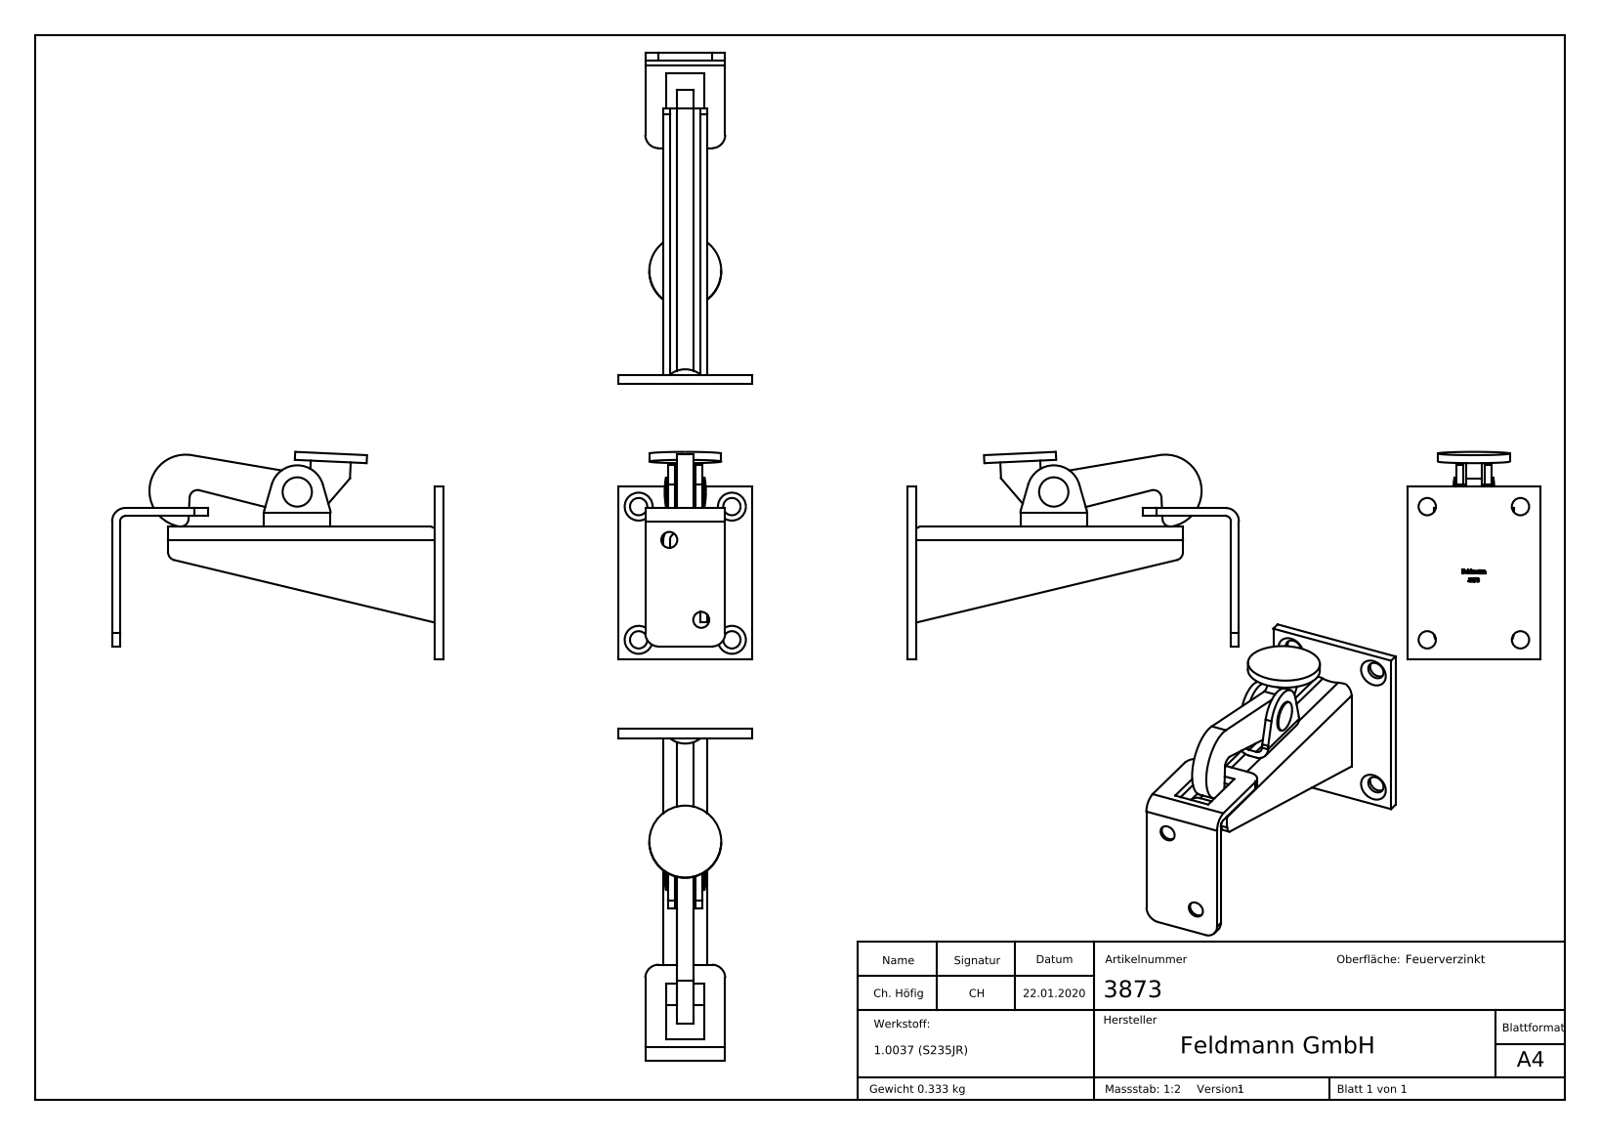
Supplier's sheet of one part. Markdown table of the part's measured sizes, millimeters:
| quantity | value |
| --- | --- |
| part name | 3873 Teil3; 3873 Teil2; 3873 Teil1_3873 Teil1; 3873 Teil2_3873 Teil2 (+5 more) |
| STEP written by | SolidWorks 2015 (CONFIG_CONTROL_DESIGN) |
| units | millimeters |
| bodies | 4 solids, 275 faces (133 planar, 41 cylindrical, 101 other) |
| overall size | 124.5 × 78.05 × 50 |
| volume | 42 723 mm³ |
| surface area | 31 831 mm² |
| round holes (diameter × count) | 6.5 × 4, 6 × 3, 5.75 × 1 |
| round bosses / shafts (diameter × count) | 27 × 1, 11 × 1, 5.5 × 1 |
| partial cylindrical surfaces (radius × count) | 5 × 11, 2.5 × 4, 3 × 3, 2 × 2, 10 × 2, 9.27 × 1, 13.59 × 1 |
| main face-to-face distances | 2.5, 14, 3.5, 2.75, 3, 5.25, 11.25, 8.75, 11.5, 16.5 |
| hole center spacings | 35, 50, 61.03, 13.73, 16.99, 24.67, 26.62, 32.31 |
